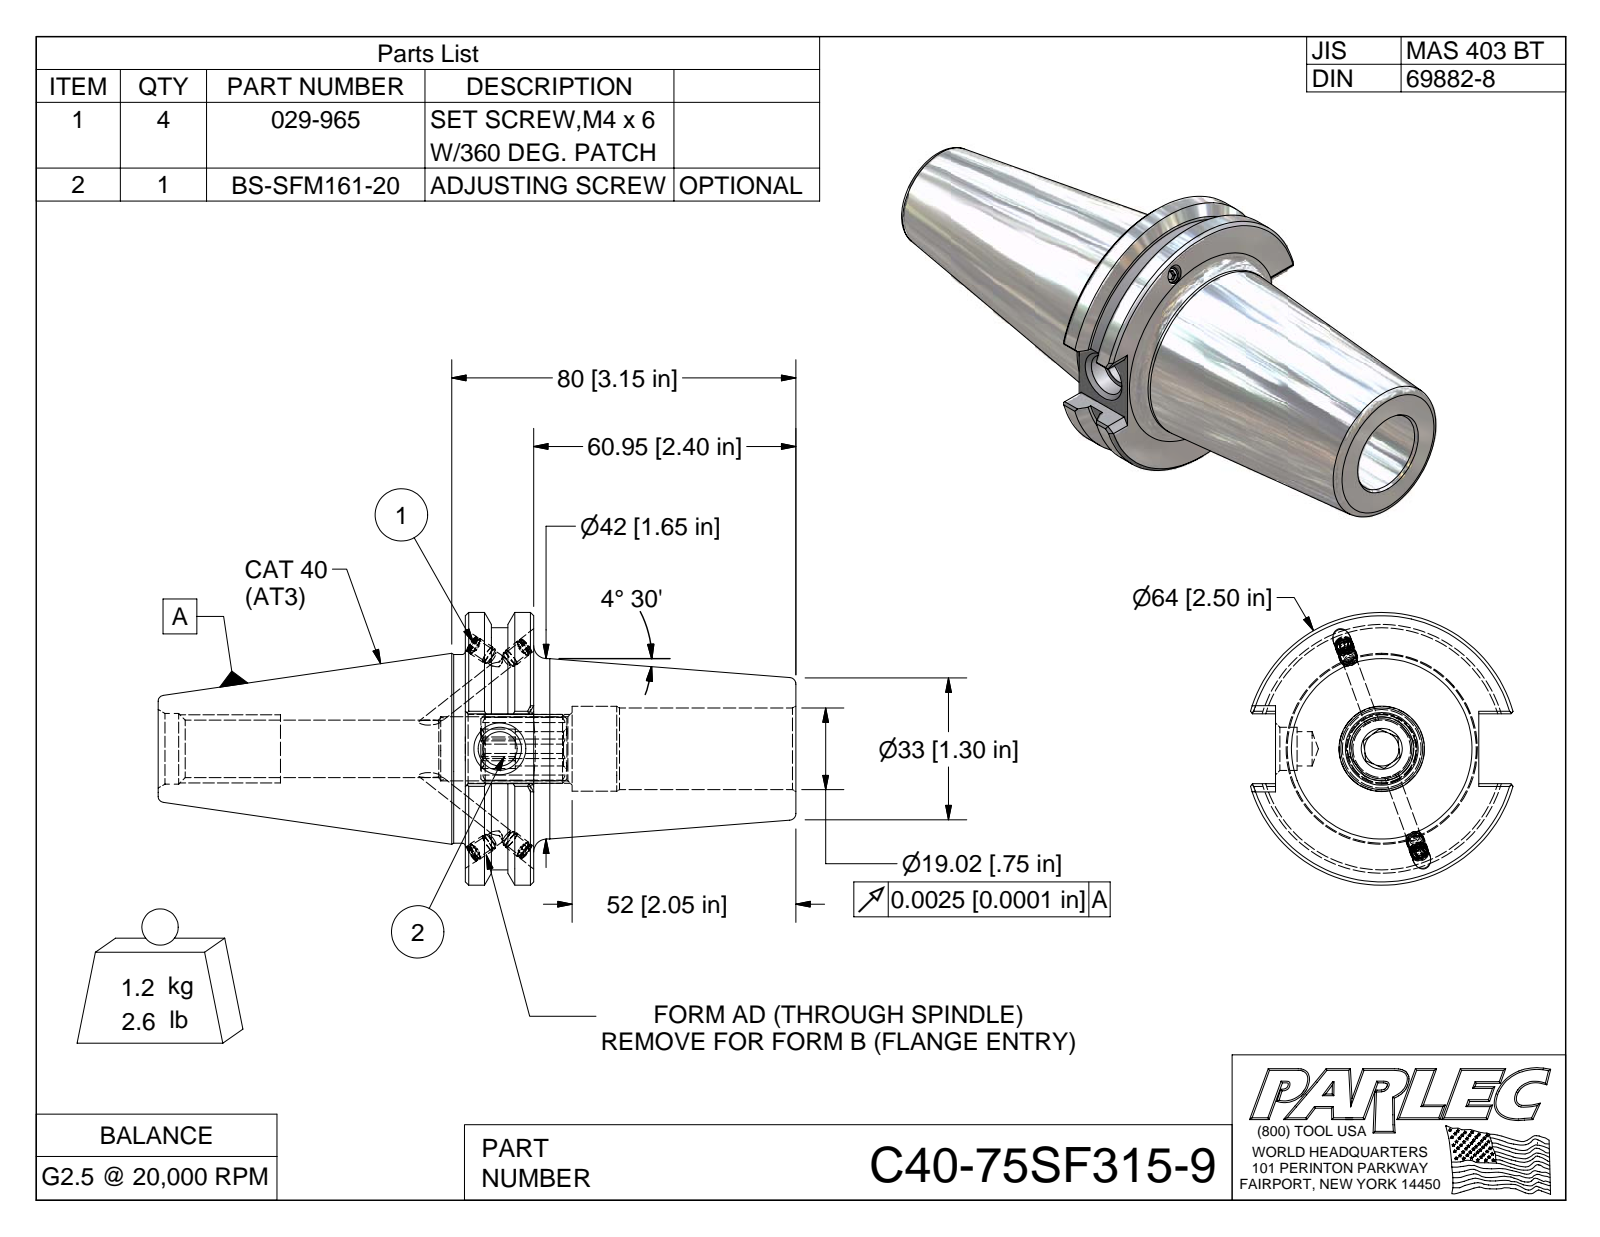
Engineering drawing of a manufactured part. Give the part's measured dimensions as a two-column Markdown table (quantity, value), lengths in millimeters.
| quantity | value |
| --- | --- |
| part name | C40-75SF315-9; C40BC-75SF315-9-1; 029-965; BS-SFM161-20 |
| STEP written by | Autodesk Inventor 2009 (AUTOMOTIVE_DESIGN) |
| units | millimeters |
| bodies | 6 solids, 173 faces (87 planar, 32 cylindrical, 54 other) |
| overall size | 148.3 × 63.5 × 61 |
| volume | 154 200 mm³ |
| surface area | 33 250 mm² |
| round holes (diameter × count) | 3.3 × 4, 4.1 × 4, 19 × 1, 19.8 × 1 |
| round bosses / shafts (diameter × count) | 4.2 × 4, 4 × 4, 63.5 × 1, 56.4 × 1, 43.9 × 1, 42 × 1 |
| partial cylindrical surfaces (radius × count) | 8 × 1 |
| main face-to-face distances | 15.9, 76.8, 61, 16.3, 14, 47.2, 71.4, 87.3, 148.3, 81.3 |
